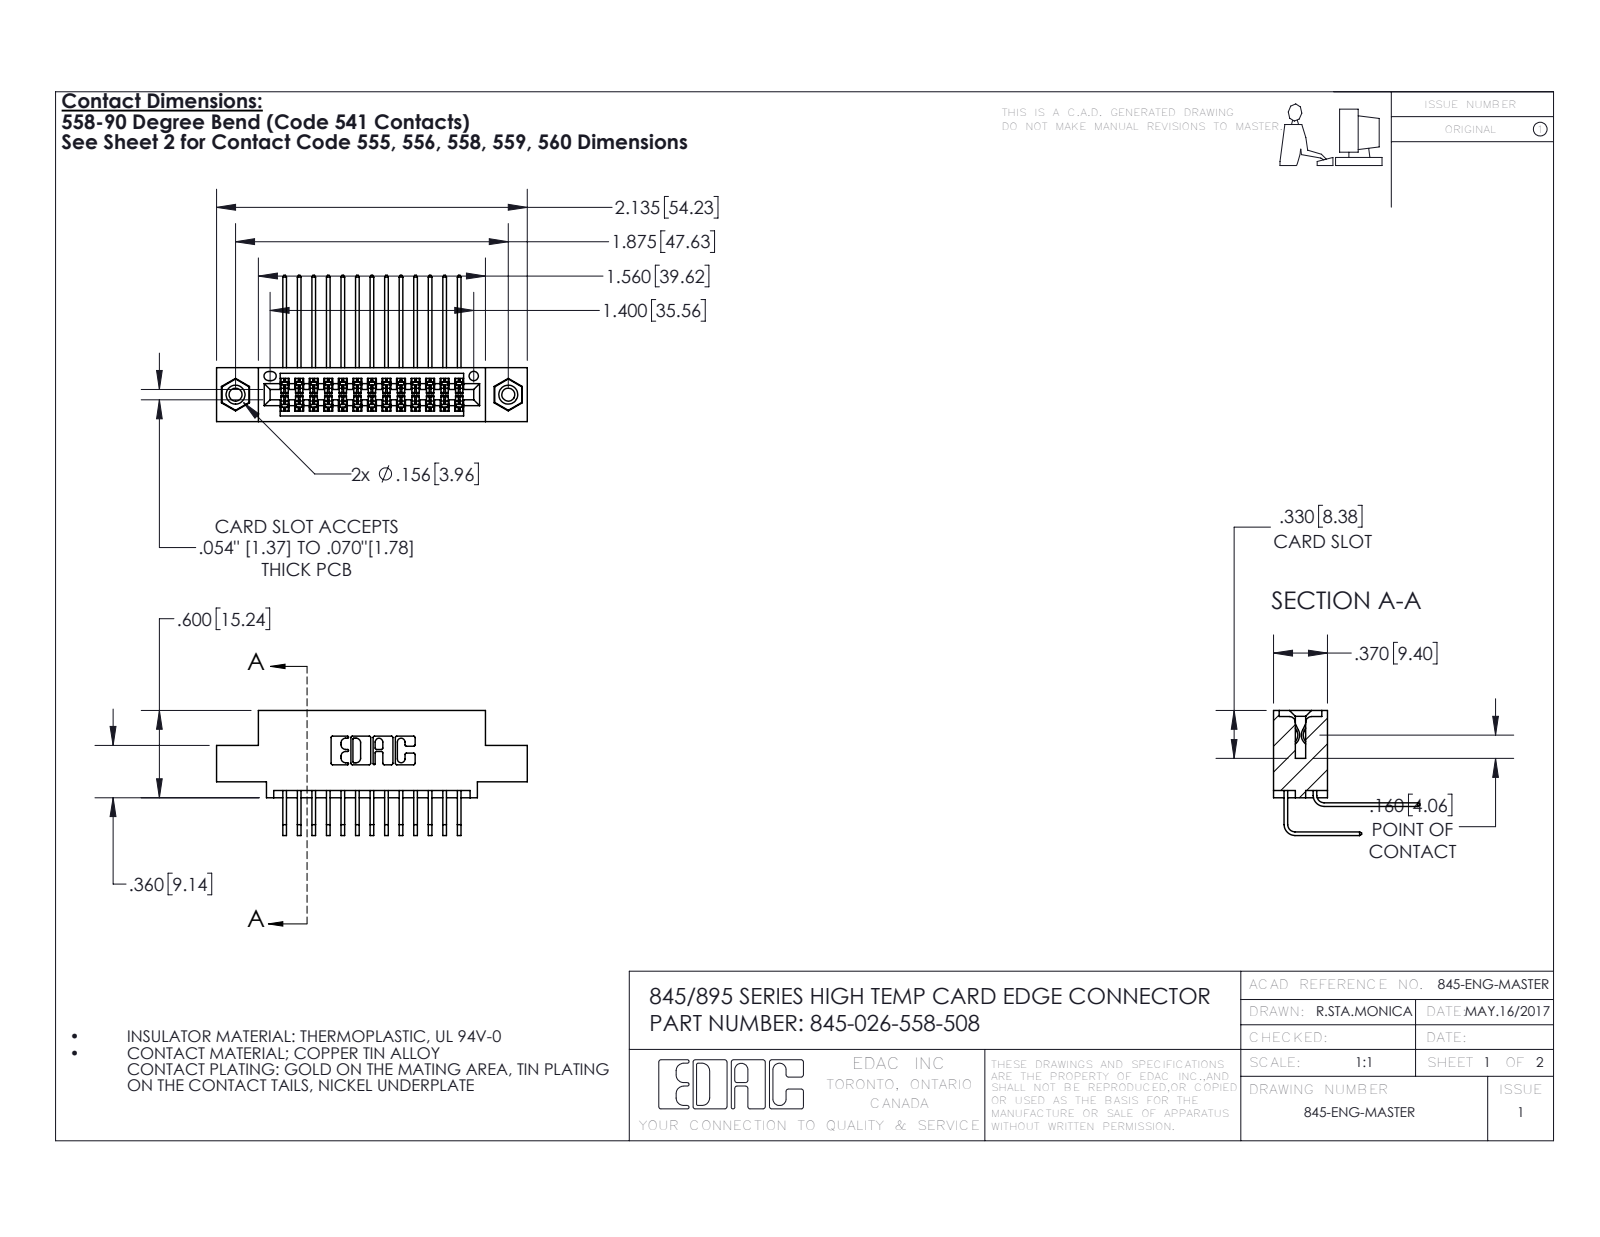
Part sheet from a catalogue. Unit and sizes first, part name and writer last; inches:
Units: inches
Overall size (bounding box): 2.135 × 1.005 × 0.859
Round holes (diameter × count): ⌀0.089 ×2, ⌀0.125 ×2, ⌀0.156 ×2, ⌀0.064 ×1
Round bosses / shafts (diameter × count): ⌀0.155 ×2
Partial cylindrical surfaces — rounded edges, fillets, slot ends (radius × count): R0.006 ×52, R0.01 ×22, R0.007 ×6, R0.031 ×6, R0.026 ×3, R0.014 ×2, R0.019 ×2, R0.022 ×2
Main face-to-face distances: 0.2, 0.072, 0.298, 0.37, 0.098, 0.272, 0.025, 0.225, 0.1, 0.16
Hole centre spacings: 0.27, 1.643, 1.875
Volume: 0.309 in³ · Surface area: 12 in²
Bodies: 29 solids, 1542 faces (1026 planar, 500 cylindrical, 16 other)
Part name (STEP PRODUCT): 345 Part_0.110 Offset - 0.156 Dia-TI; 345-026-558-508; 345-250-001_345-250-003-102; 345-292-001_558 559 Tail - 1 (+1 more)
STEP written by: SolidWorks 2016 (CONFIG_CONTROL_DESIGN)
